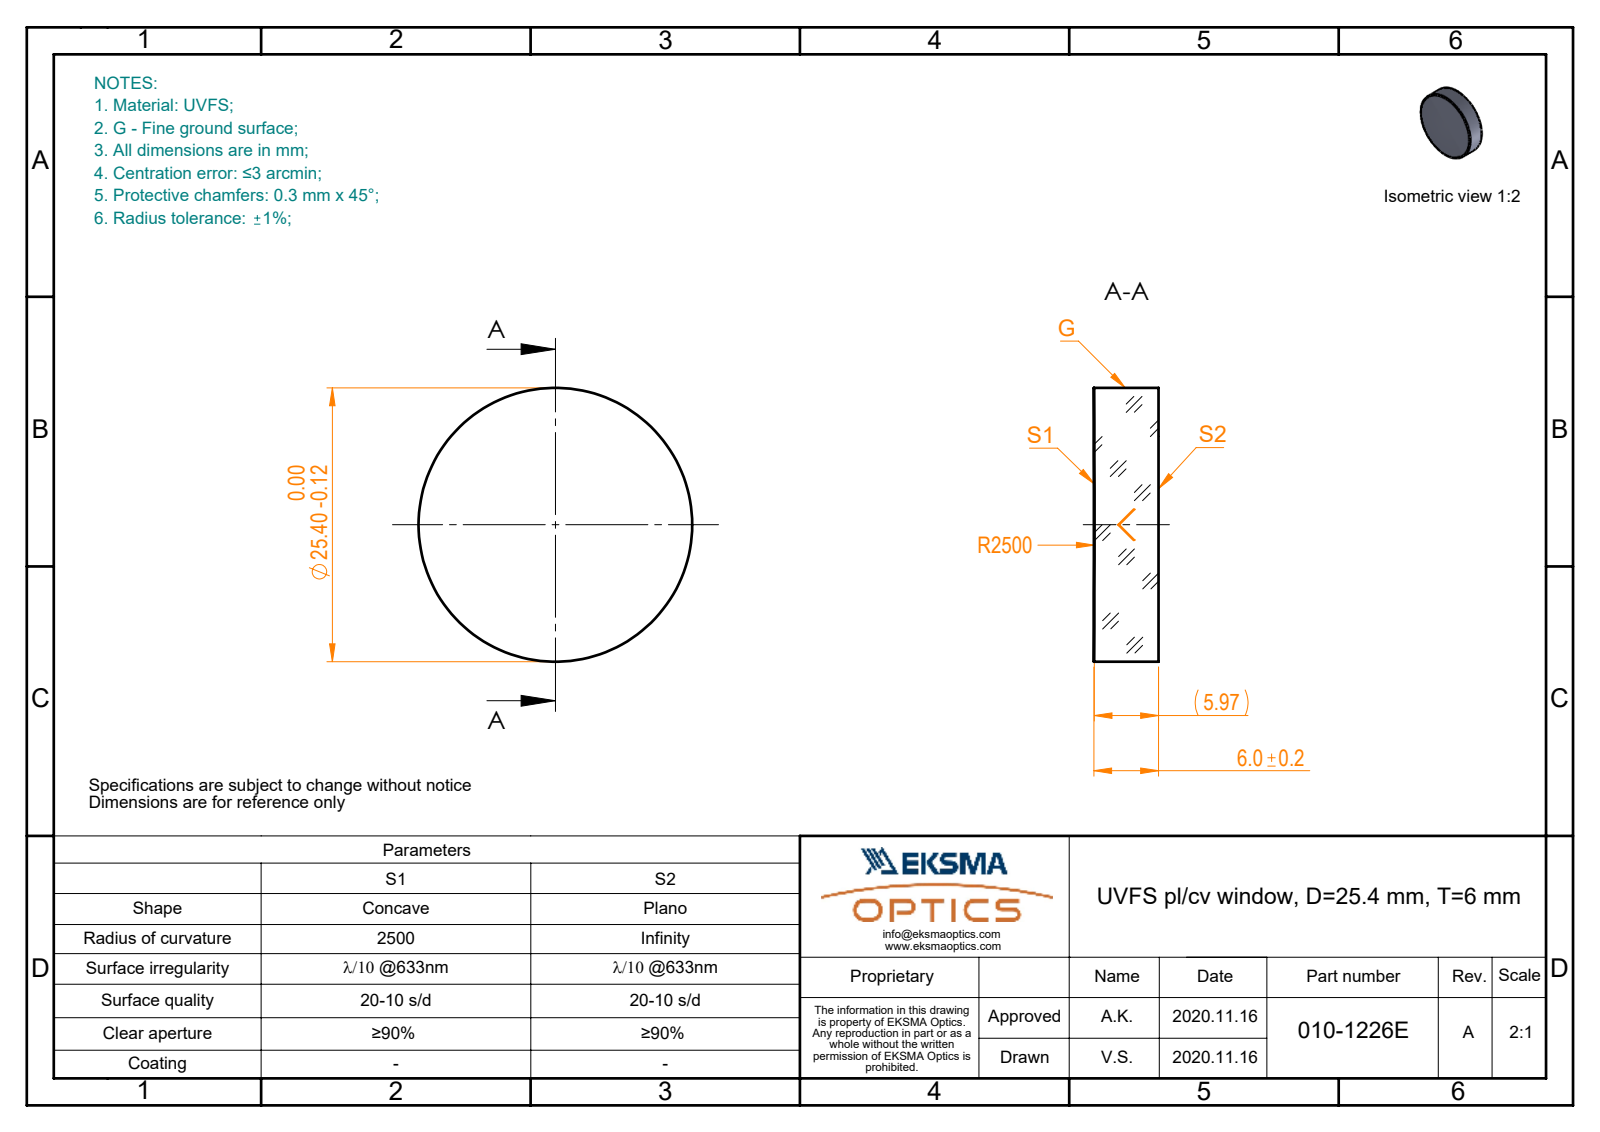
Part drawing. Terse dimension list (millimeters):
name: 010-1226E_UVFS_PCV_window
written by: SolidWorks 2019 (CONFIG_CONTROL_DESIGN)
unit: mm
bodies: 1 solid, 5 faces (1 planar, 2 cylindrical, 2 other)
size: 25.4 × 25.4 × 6
volume: 3 032 mm³; area: 1 492 mm²
bosses: 1× ⌀25.4
